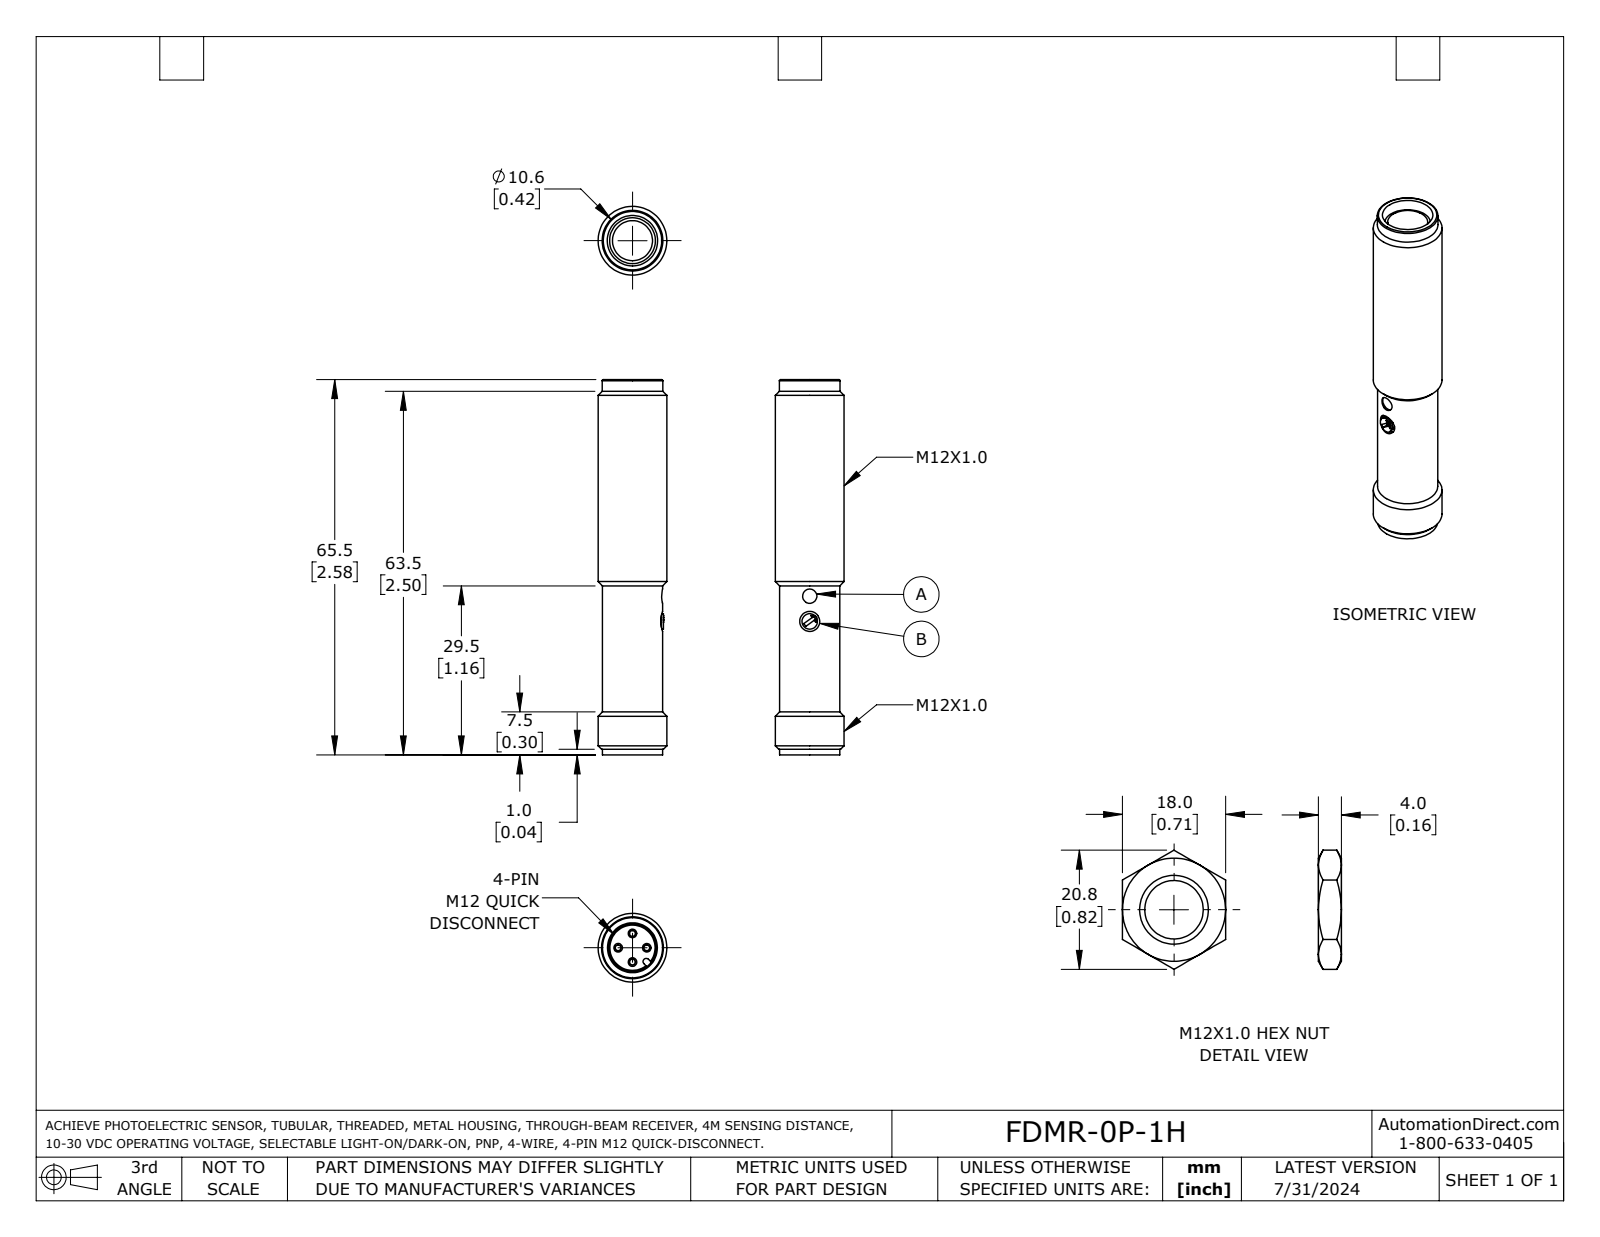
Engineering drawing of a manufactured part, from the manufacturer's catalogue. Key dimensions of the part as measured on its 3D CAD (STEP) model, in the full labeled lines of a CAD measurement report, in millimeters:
Part name (STEP PRODUCT): DME_1H_fig
STEP written by: SolidWorks 2023 (AUTOMOTIVE_DESIGN)
Units: millimetres
Bodies: 1 solid, 60 faces (25 planar, 18 cylindrical, 17 other)
Overall size (bounding box): 65.5 × 12 × 12
Volume: 6 210 mm³ · Surface area: 2 992 mm²
Round holes (diameter × count): ⌀2.5 ×1, ⌀3 ×1, ⌀3.5 ×1, ⌀8.3 ×1
Round bosses / shafts (diameter × count): ⌀1 ×4, ⌀12 ×1, ⌀10.6 ×1, ⌀10.5 ×1, ⌀7 ×1, ⌀2.7 ×1, ⌀2.5 ×1
Partial cylindrical surfaces — rounded edges, fillets, slot ends (radius × count): R0.6 ×1
Main face-to-face distances: 8.9, 65.5, 56.6, 1, 0.5, 63.8, 54.9, 1.7, 2.4, 2.9
Hole centre spacings: 4.4
